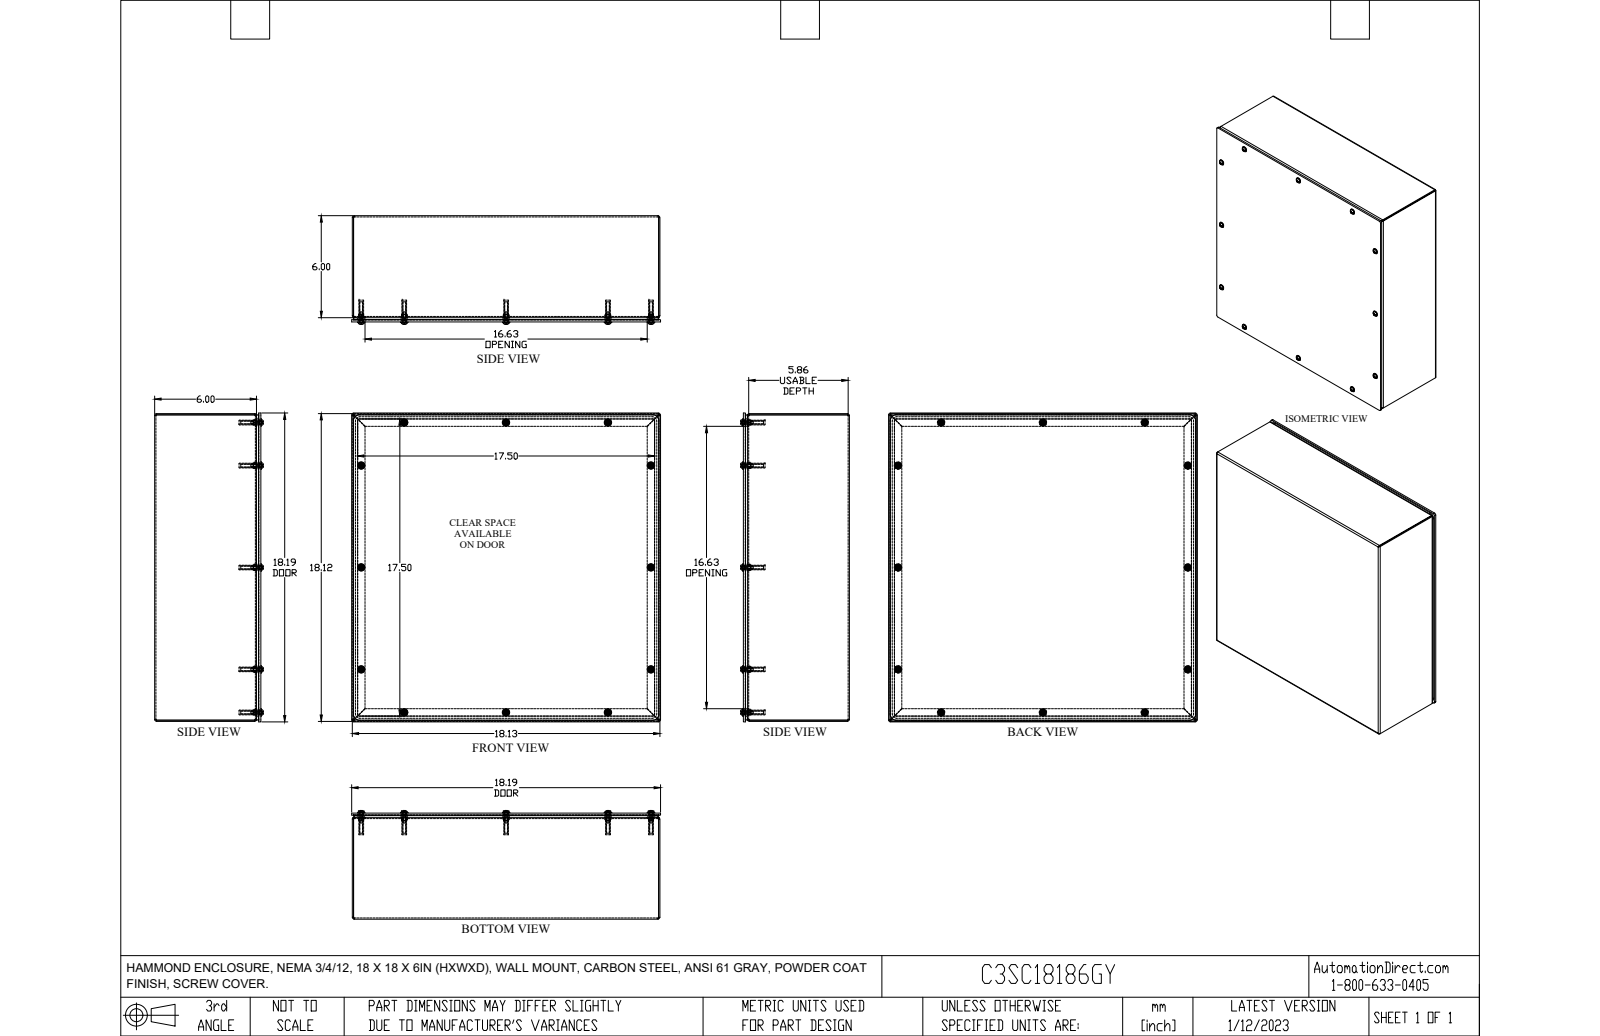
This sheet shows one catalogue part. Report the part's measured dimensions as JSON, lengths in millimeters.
{"part_name": "C3SC18186GY", "step_written_by": "SolidWorks 2021 (AUTOMOTIVE_DESIGN)", "units": "millimeters", "bodies": {"solids": 40, "faces": 1278, "planar": 810, "cylindrical": 228, "other": 240}, "overall_size": [462, 462, 162.6], "volume_mm3": 2573000, "surface_area_mm2": 2575000, "round_holes": [[4, 12], [4.1, 12], [6.4, 12]], "round_bosses_or_shafts": [[11.2, 12], [9.9, 12], [7, 12], [6.1, 12], [4.8, 12], [3.8, 12]], "partial_cylinders_radius": [[4.1, 12], [0.9, 8], [1, 8], [2.7, 8], [2.8, 8], [3.2, 8], [3.2, 4], [9.5, 4]], "face_to_face_distances": [1.8, 1.8, 458.5, 3.2, 158.8, 155.6, 157, 153.8, 156.9, 153.7], "hole_center_spacings": [152.4, 226.2, 374.8, 428.2, 459.7, 433.7, 91.2, 304.8]}
